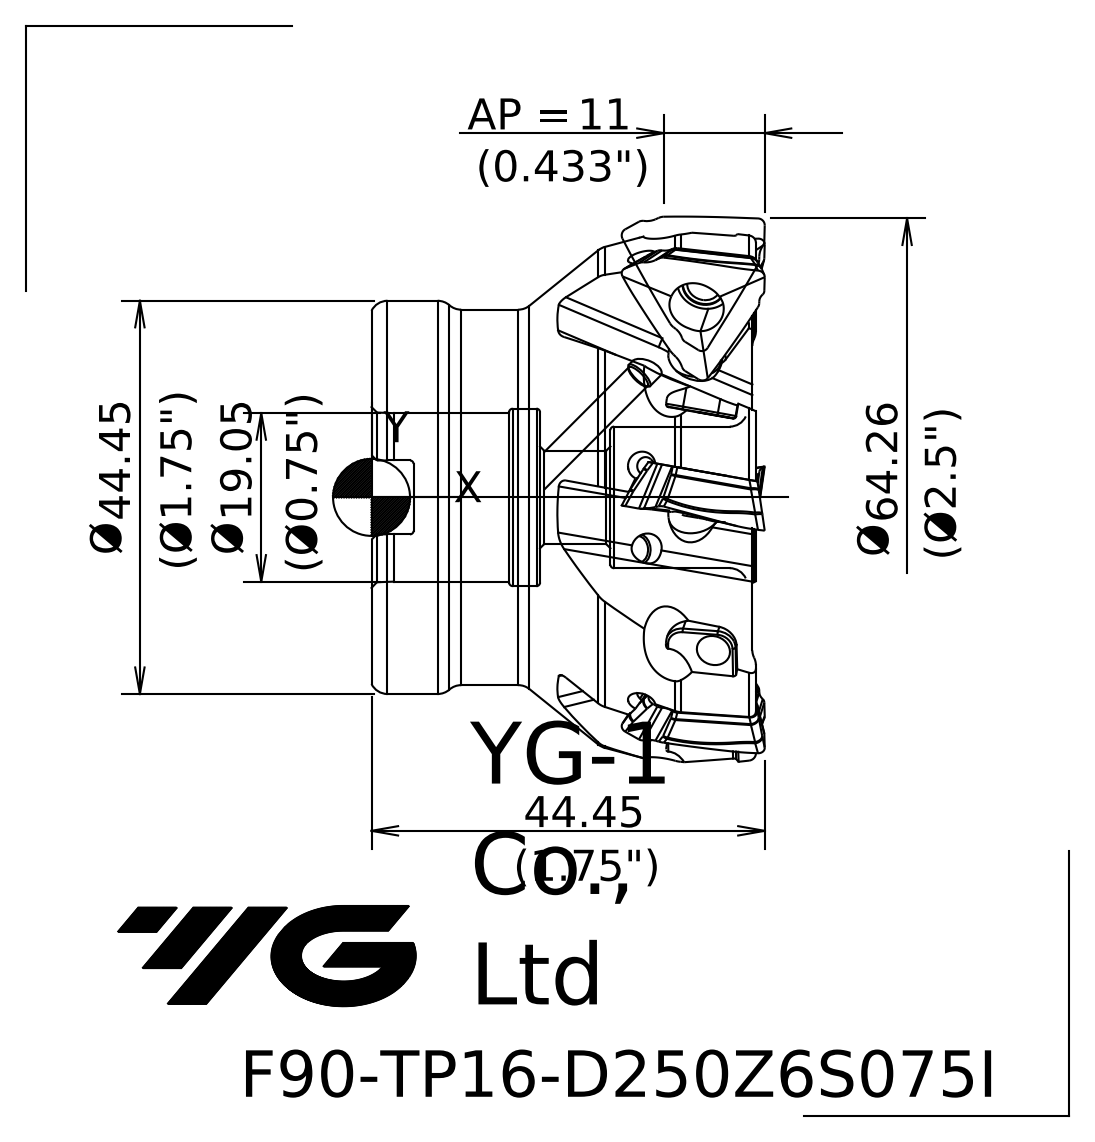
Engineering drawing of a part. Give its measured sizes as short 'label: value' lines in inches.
name: 10223BFCFCF2poxr
written by: SIEMENS PLM Software NX 10.0 (AP203_CONFIGURATION_CONTROLLED_3D_DESIGN_OF_MECHANICAL_PARTS_AND_ASSEMBLIES_MIM_LF)
unit: in
bodies: 1 solid, 73 faces (17 planar, 10 cylindrical, 46 other)
size: 2.504 × 2.504 × 1.75
volume: 4.868 in³; area: 34 in²
holes: 1× ⌀0.413, 1× ⌀0.63, 1× ⌀0.75, 1× ⌀0.789
bosses: 1× ⌀1.75, 1× ⌀1.671
rounds: 2× R0.016
face distances: 1.695, 1.508, 0.187, 0.945, 0.563, 0.75, 0.329, 0.016, 0.961, 1.524
